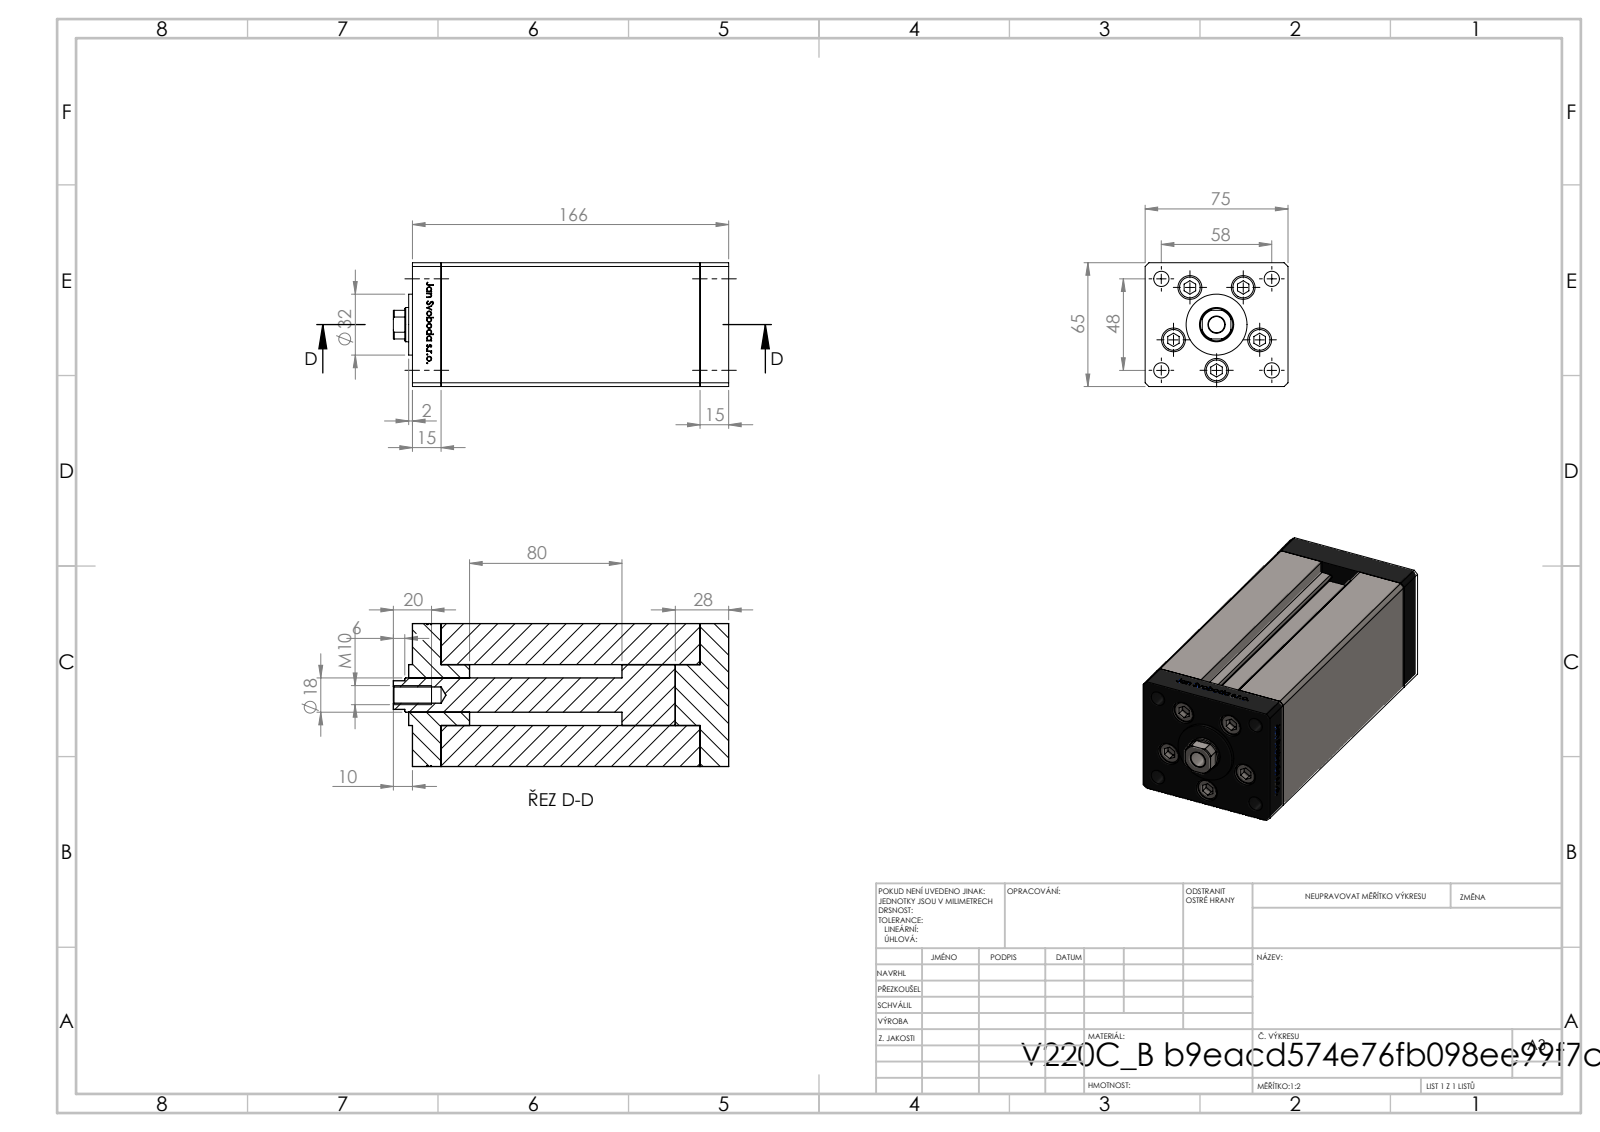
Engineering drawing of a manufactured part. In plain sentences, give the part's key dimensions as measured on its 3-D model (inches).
The part is named "V220C_FRONT_B; V220C_B MIDDLE; ALLEN BOLT; V220C BACK_B (+1 more)". Its 3-D file was written by "SolidWorks 2019 (CONFIG_CONTROL_DESIGN)". It is 14 solids with 1183 faces: 462 planar, 147 cylindrical and 574 other. Overall it measures 6.929 by 2.953 by 2.559 inches. Its volume is 44.09 cubic inches and its surface area 197.4 square inches. Round holes: 5 of diameter 0.354, 5 of diameter 0.492, 4 of diameter 0.315, 2 of diameter 0.079, 2 of diameter 0.518, 1 of diameter 0.335, 1 of diameter 0.709. Round bosses or shafts: 5 of diameter 0.315, 1 of diameter 1.26. Partial cylindrical surfaces (rounded edges, fillets, slot ends): 2 of radius 0.037, 1 of radius 0.335. The main face-to-face distances are 2.953, 2.559, 0.591, 5.354, 5.945, 6.535, 1.102, 0.512, 2.146, 0.413. The hole center spacings are 0.945, 1.482, 0.617, 0.678, 1.091, 1.135, 1.142, 1.285.
